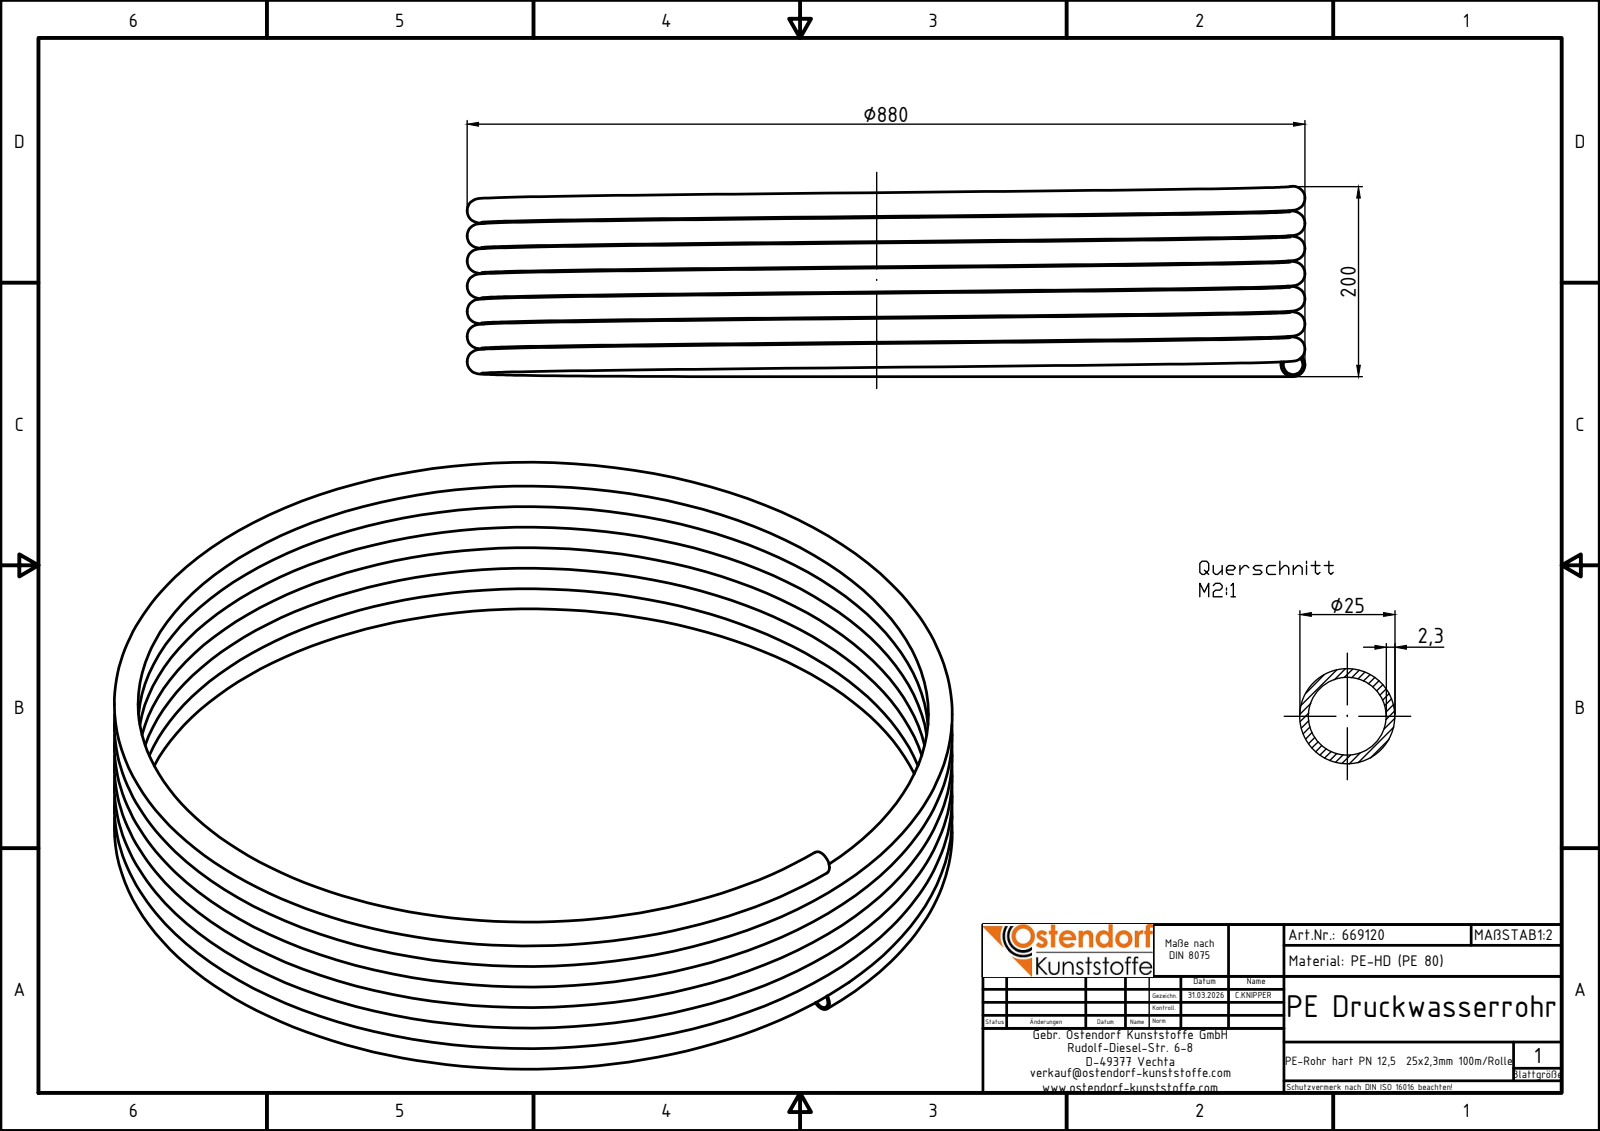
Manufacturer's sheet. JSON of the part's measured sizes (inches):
{"part_name": "669120z", "step_written_by": "Autodesk Inventor 2024 (AUTOMOTIVE_DESIGN)", "units": "inches", "bodies": {"solids": 1, "faces": 7, "planar": 3, "cylindrical": 0, "other": 4}, "overall_size": [34.646, 34.646, 7.875], "volume_in3": 186.8, "surface_area_in2": 4109}
